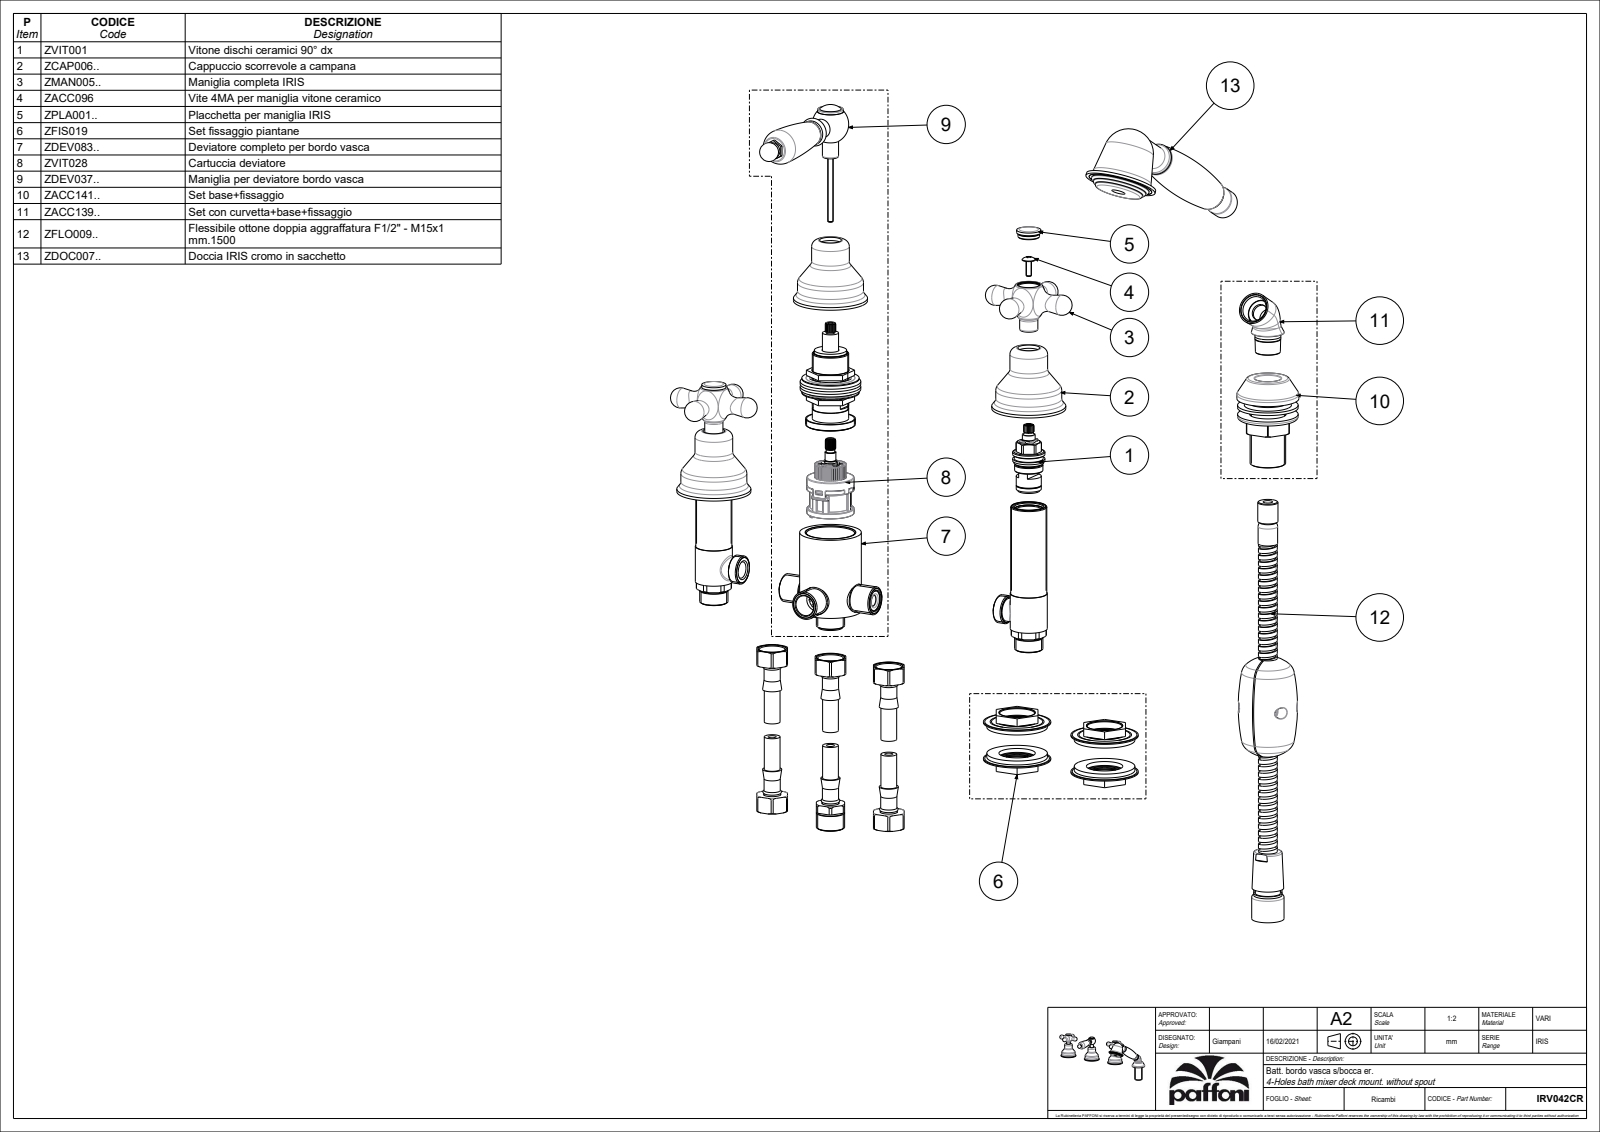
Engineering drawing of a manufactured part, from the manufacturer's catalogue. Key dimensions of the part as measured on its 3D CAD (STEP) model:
Part name (STEP PRODUCT): IRV042CR
STEP written by: CREO PARAMETRIC BY PTC INC, 2020044 (CONFIG_CONTROL_DESIGN)
Units: millimetres
Bodies: 4 solids, 296 faces (33 planar, 60 cylindrical, 203 other)
Overall size (bounding box): 362.5 × 225.92 × 124.66
Volume: 413 347 mm³ · Surface area: 81 614 mm²
Round holes (diameter × count): ⌀14.5 ×1
Round bosses / shafts (diameter × count): ⌀55 ×3, ⌀49 ×3, ⌀28 ×3, ⌀18 ×3, ⌀14 ×2, ⌀13.5 ×2, ⌀53 ×1, ⌀46 ×1
Main face-to-face distances: 6, 46.5, 2, 15.7, 30.8, 4, 1, 103.99, 104.99, 15
